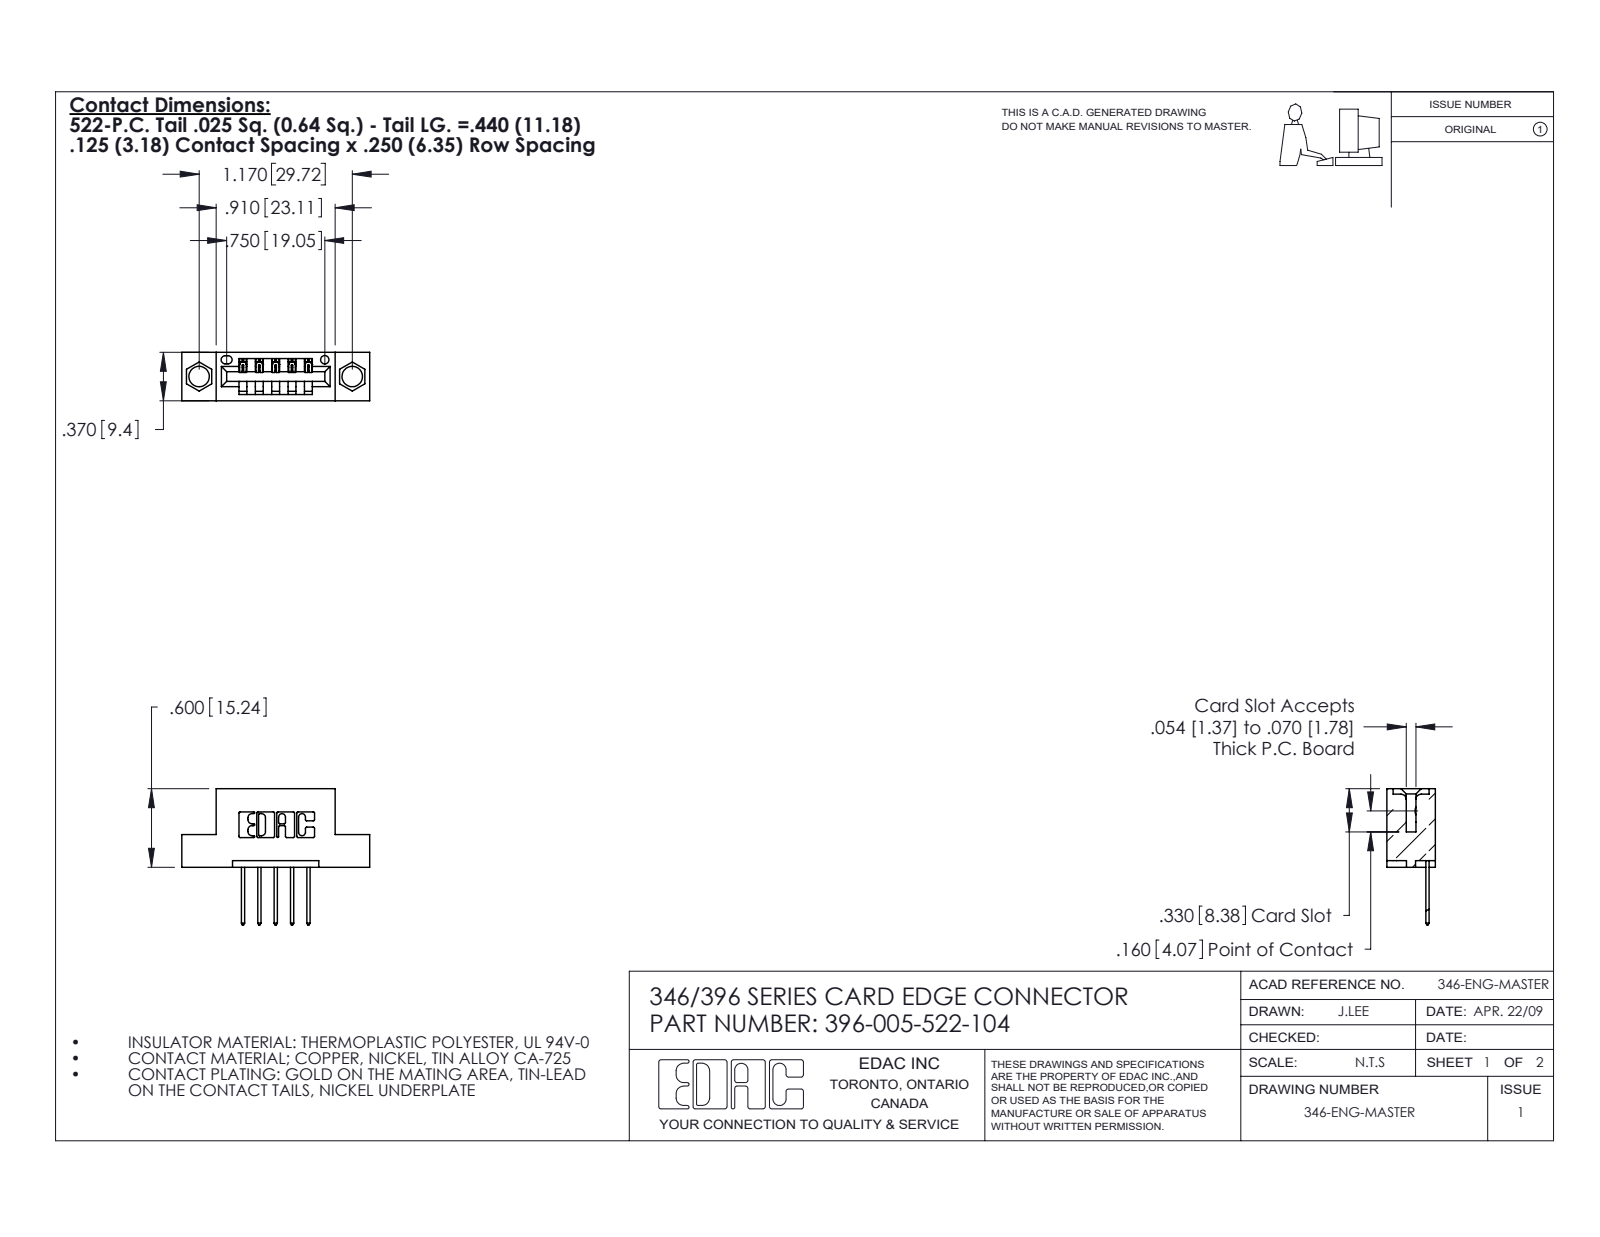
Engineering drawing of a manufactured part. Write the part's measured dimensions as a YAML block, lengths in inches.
part_name: "346 Part_Flush Mounting Lugs - 0.156 Dia-TH; 396-005-522-104; 345-292-001_345-293-122"
step_written_by: "SolidWorks 2020 (CONFIG_CONTROL_DESIGN)"
units: inches
bodies: {solids: 6, faces: 426, planar: 290, cylindrical: 136, other: 0}
overall_size: [1.435, 1.04, 0.37]
volume: 0.191
surface_area: 5.219
round_holes:
  - {diameter: 0.156, count: 2}
  - {diameter: 0.064, count: 1}
partial_cylinders:
  - {radius: 0.01, count: 22}
  - {radius: 0.006, count: 10}
  - {radius: 0.01, count: 10}
  - {radius: 0.007, count: 6}
  - {radius: 0.031, count: 6}
  - {radius: 0.026, count: 3}
  - {radius: 0.031, count: 2}
  - {radius: 0.04, count: 2}
face_to_face_distances: [0.25, 0.37, 0.048, 0.322, 0.148, 0.222, 0.1, 0.174, 0.55, 0.072]
hole_center_spacings: [0.246, 0.969, 1.17]
